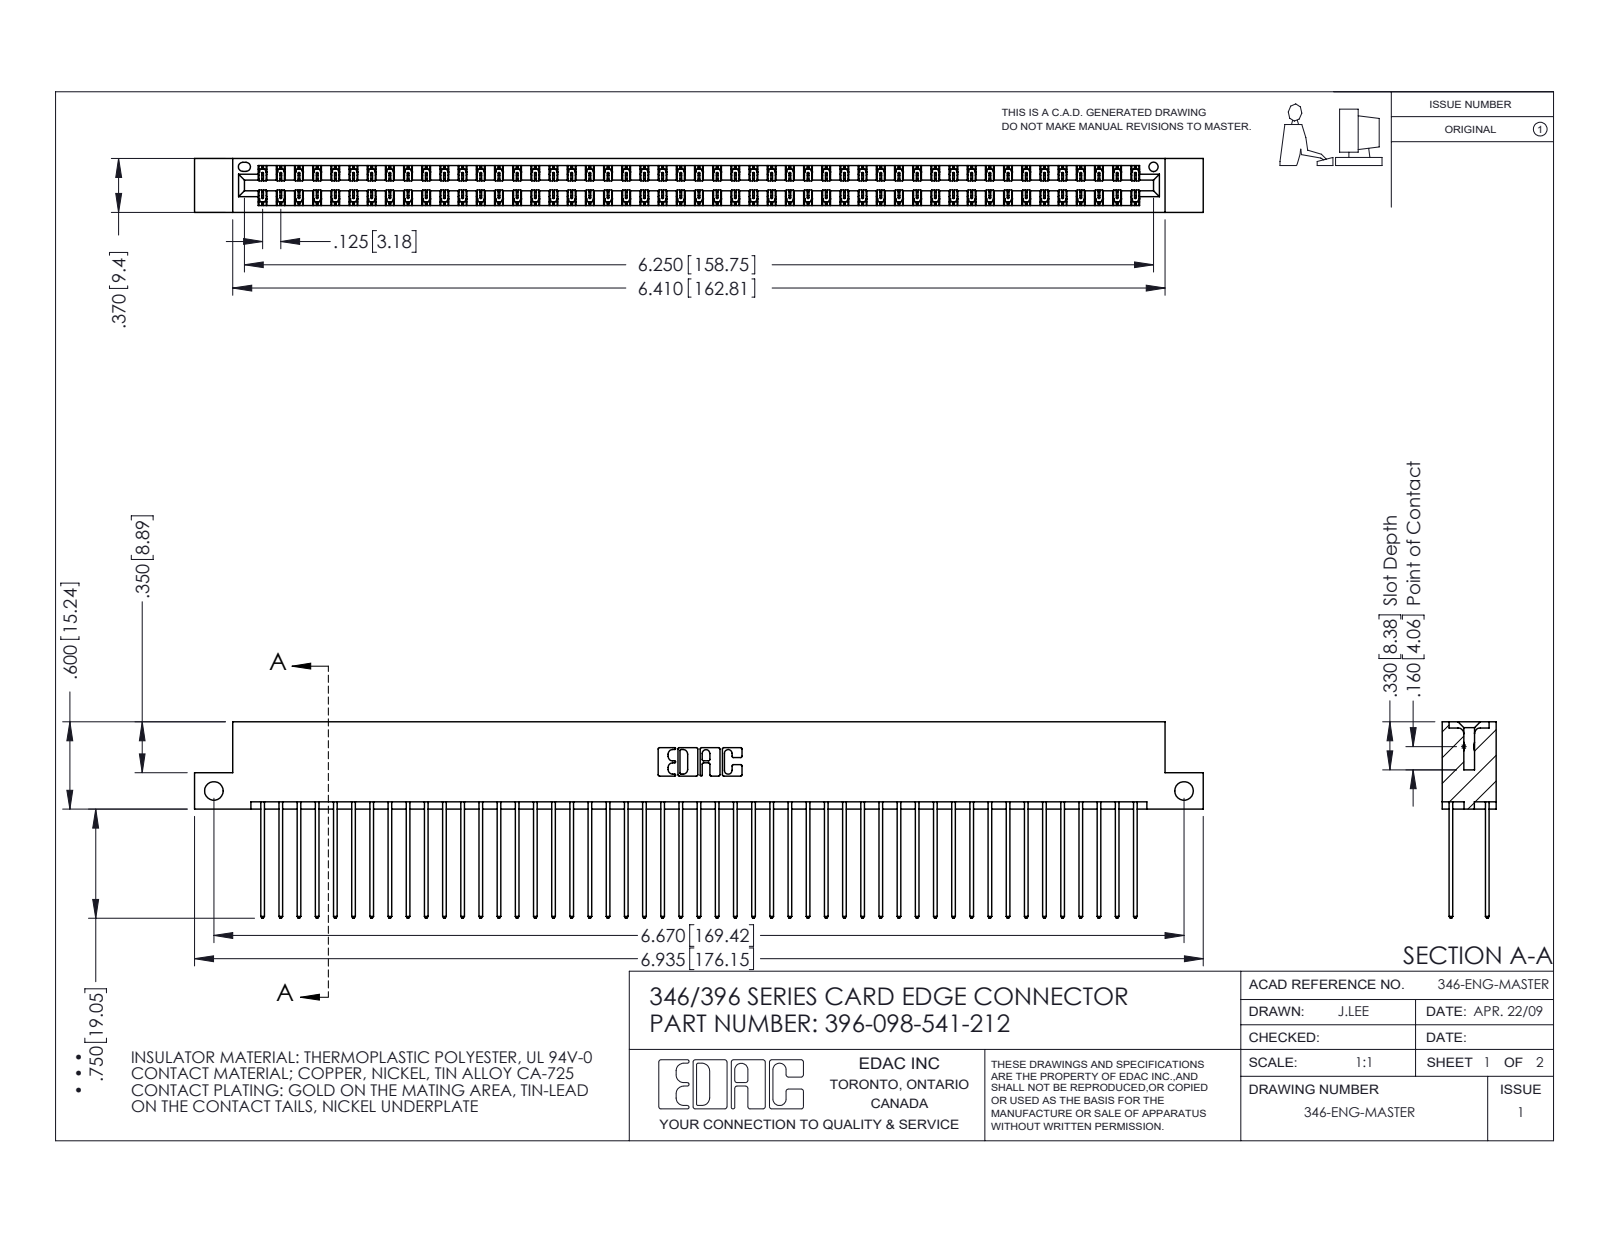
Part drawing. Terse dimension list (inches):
name: 396-098-541-212; 345-292-001_345-293-141; 346 Part_Flush Mounting Lugs - Side Mount
written by: SolidWorks 2016 (CONFIG_CONTROL_DESIGN)
unit: in
bodies: 99 solids, 5218 faces (3506 planar, 1712 cylindrical, 0 other)
size: 6.935 × 1.35 × 0.37
volume: 1.08 in³; area: 41.86 in²
holes: 2× ⌀0.128, 1× ⌀0.064
rounds: 147× R0.006, 98× R0.01, 22× R0.01, 6× R0.007, 6× R0.031, 3× R0.026, 2× R0.014, 2× R0.022
face distances: 0.048, 0.322, 0.25, 0.072, 0.298, 0.025, 0.37, 0.275, 0.225, 0.148
hole spacings: 6.67
